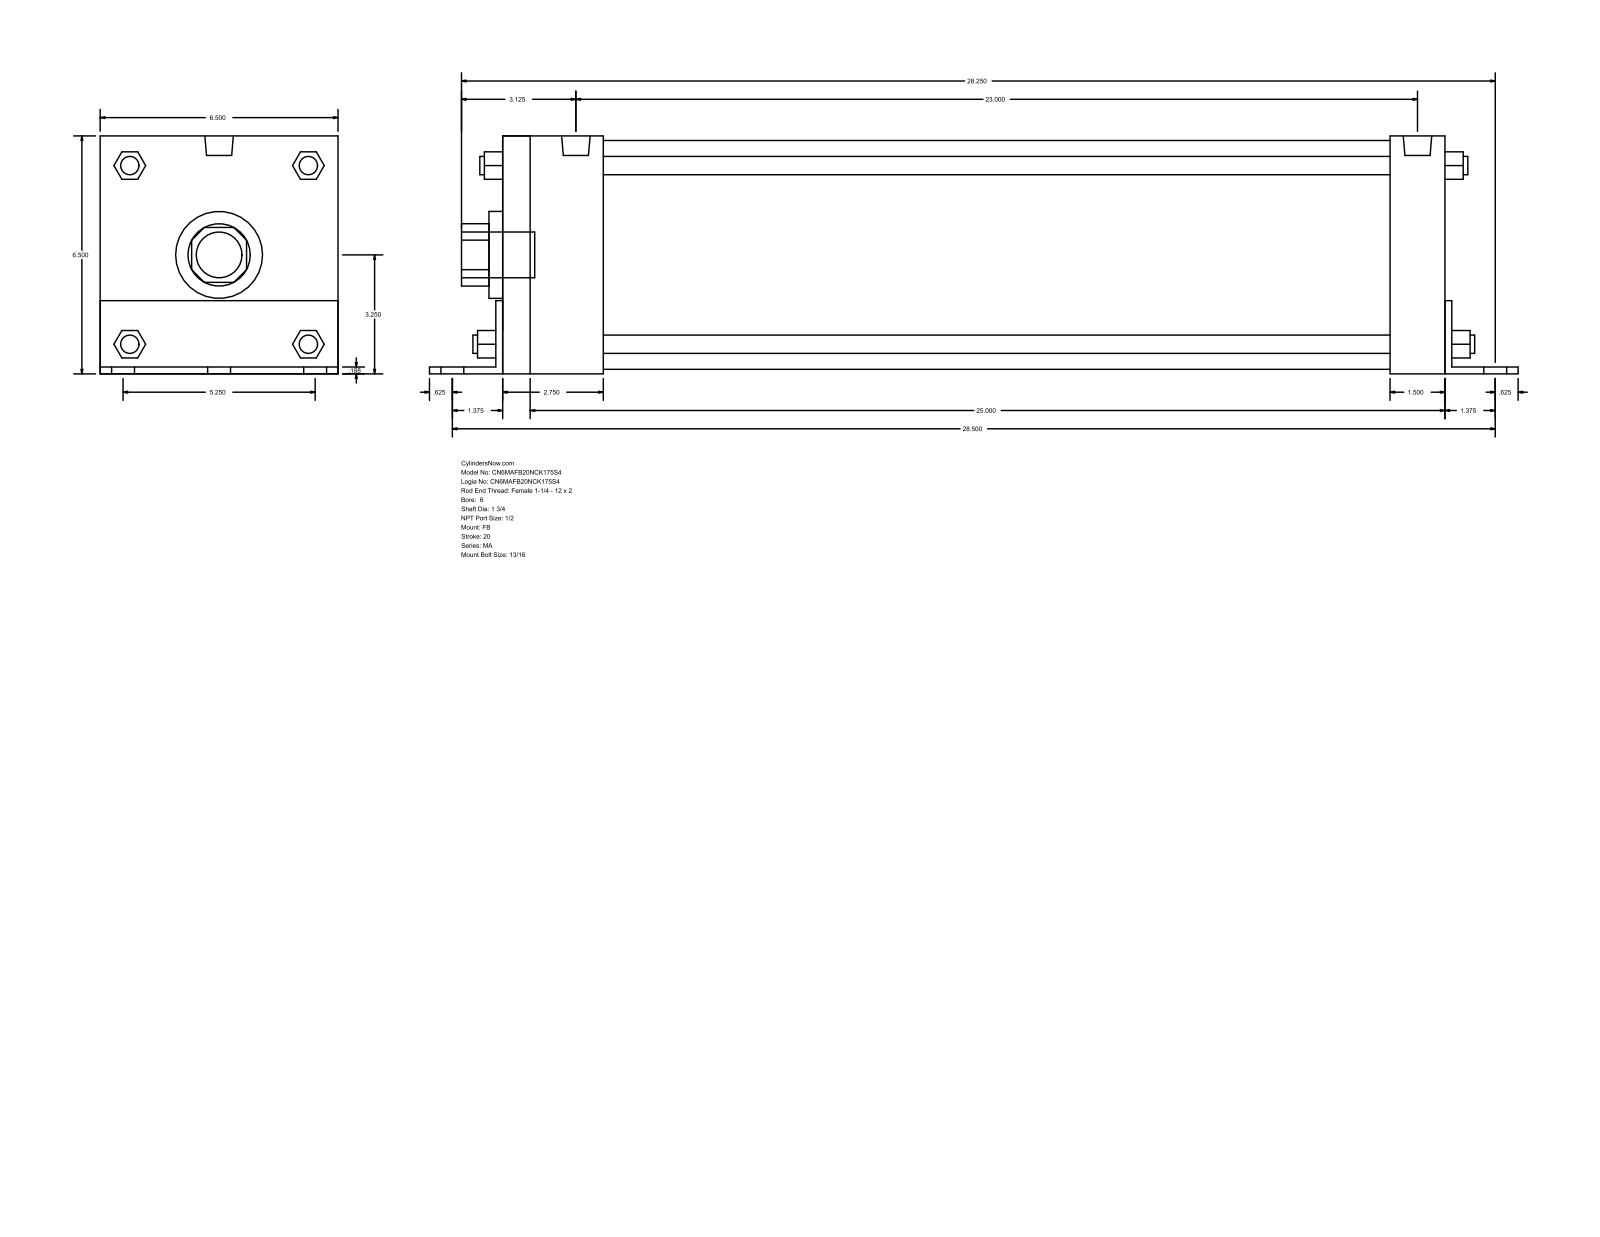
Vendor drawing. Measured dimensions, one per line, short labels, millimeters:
name: MA_FB__0600_1.75
written by: GSSL Pune (CONFIG_CONTROL_DESIGN)
unit: mm
bodies: 0 solids, 140 faces (105 planar, 35 cylindrical, 0 other)
size: 755.65 × 165.15 × 165.1
holes: 1× ⌀44.45, 1× ⌀60.33, 1× ⌀158.75
bosses: 6× ⌀20.64, 4× ⌀17.46, 4× ⌀12.7, 2× ⌀19.77, 1× ⌀31.75
rounds: 1× R21.63, 1× R32.05
face distances: 165.1, 4.76, 654.05, 165.15, 4.71, 160.39, 38.1, 4.77, 658.82, 658.81
